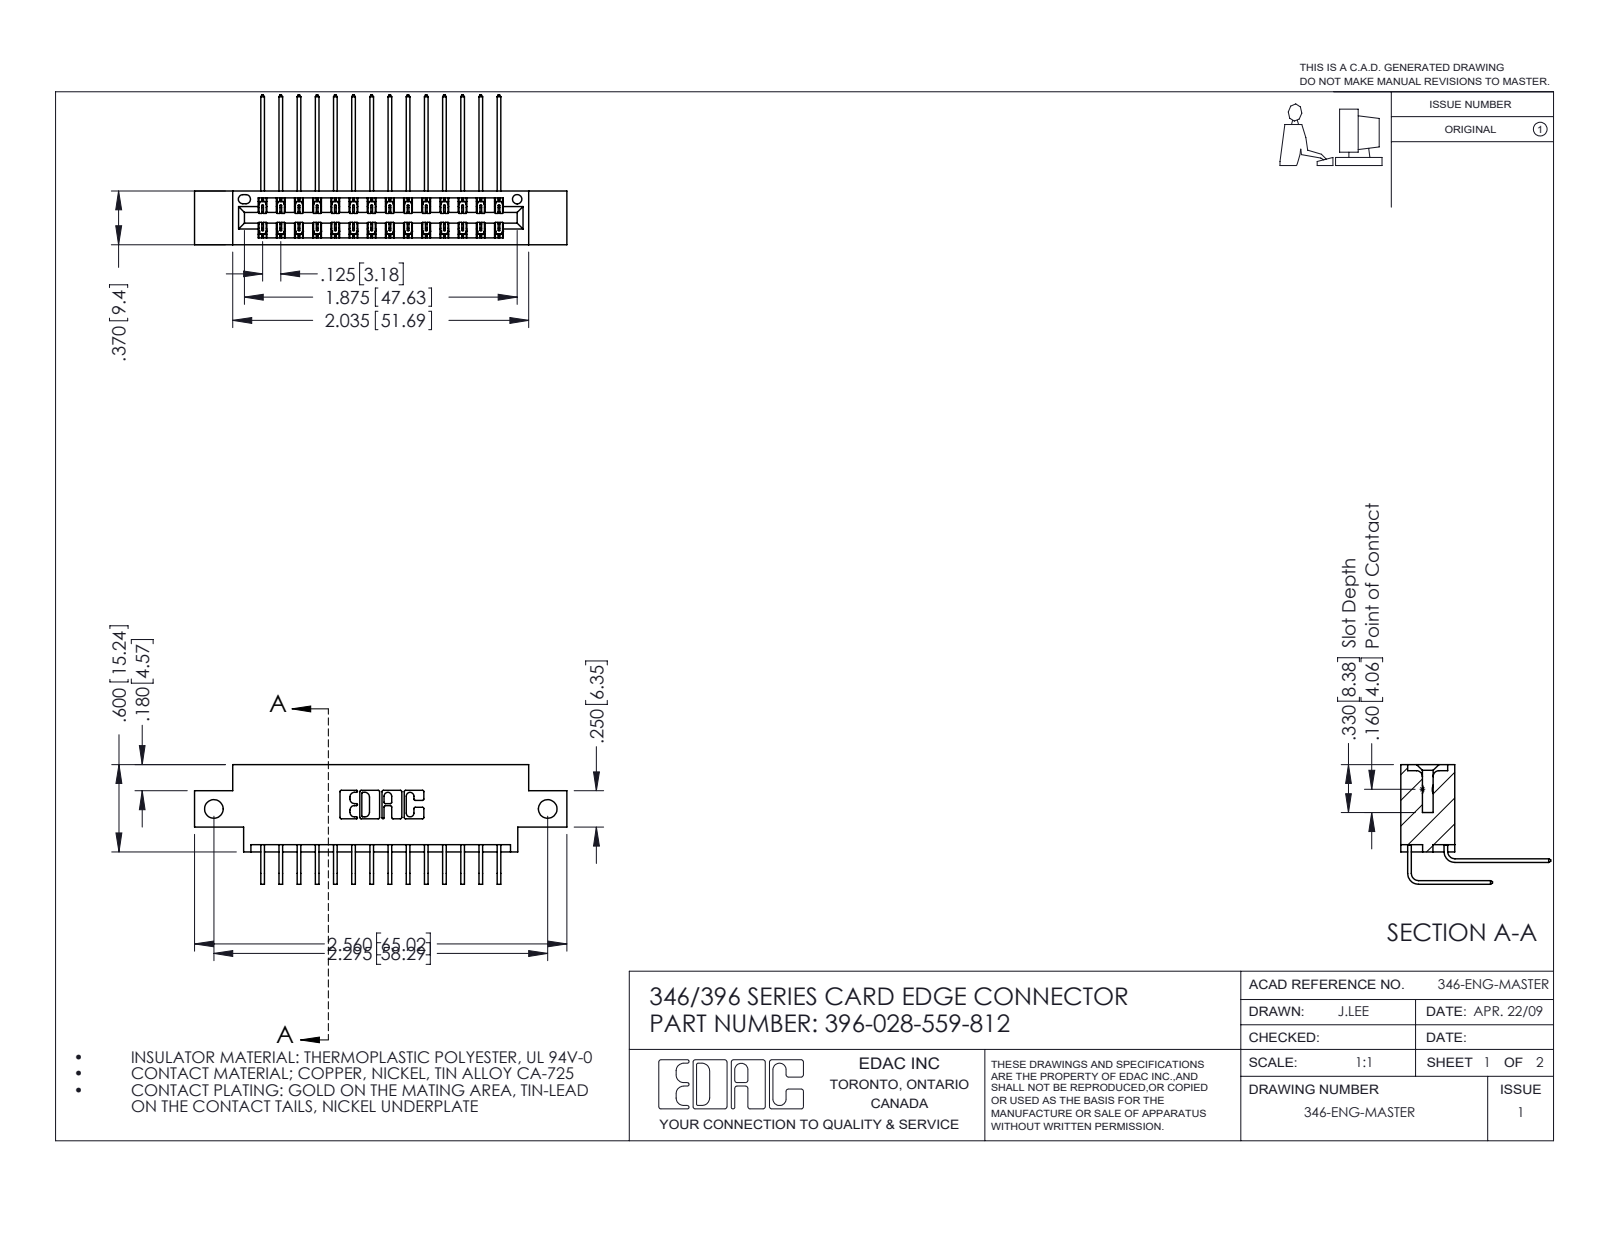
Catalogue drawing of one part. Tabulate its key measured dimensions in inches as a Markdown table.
| quantity | value |
| --- | --- |
| part name | 396-028-559-812; 346 Part_0.170 Offset - Side Mount; 345-292-001_559 Tail - 2; 345-292-001_558 559 Tail - 1 |
| STEP written by | SolidWorks 2016 (CONFIG_CONTROL_DESIGN) |
| units | inches |
| bodies | 29 solids, 1638 faces (1116 planar, 522 cylindrical, 0 other) |
| overall size | 2.56 × 1.03 × 0.823 |
| volume | 0.369 in³ |
| surface area | 13.46 in² |
| round holes (diameter × count) | 0.128 × 2, 0.064 × 1 |
| partial cylindrical surfaces (radius × count) | 0.006 × 42, 0.01 × 22, 0.007 × 6, 0.031 × 6, 0.026 × 3, 0.014 × 2, 0.022 × 2, 0.024 × 2 |
| main face-to-face distances | 0.048, 0.322, 0.37, 0.25, 0.025, 0.072, 0.298, 0.275, 0.15, 0.148 |
| hole center spacings | 2.295 |
